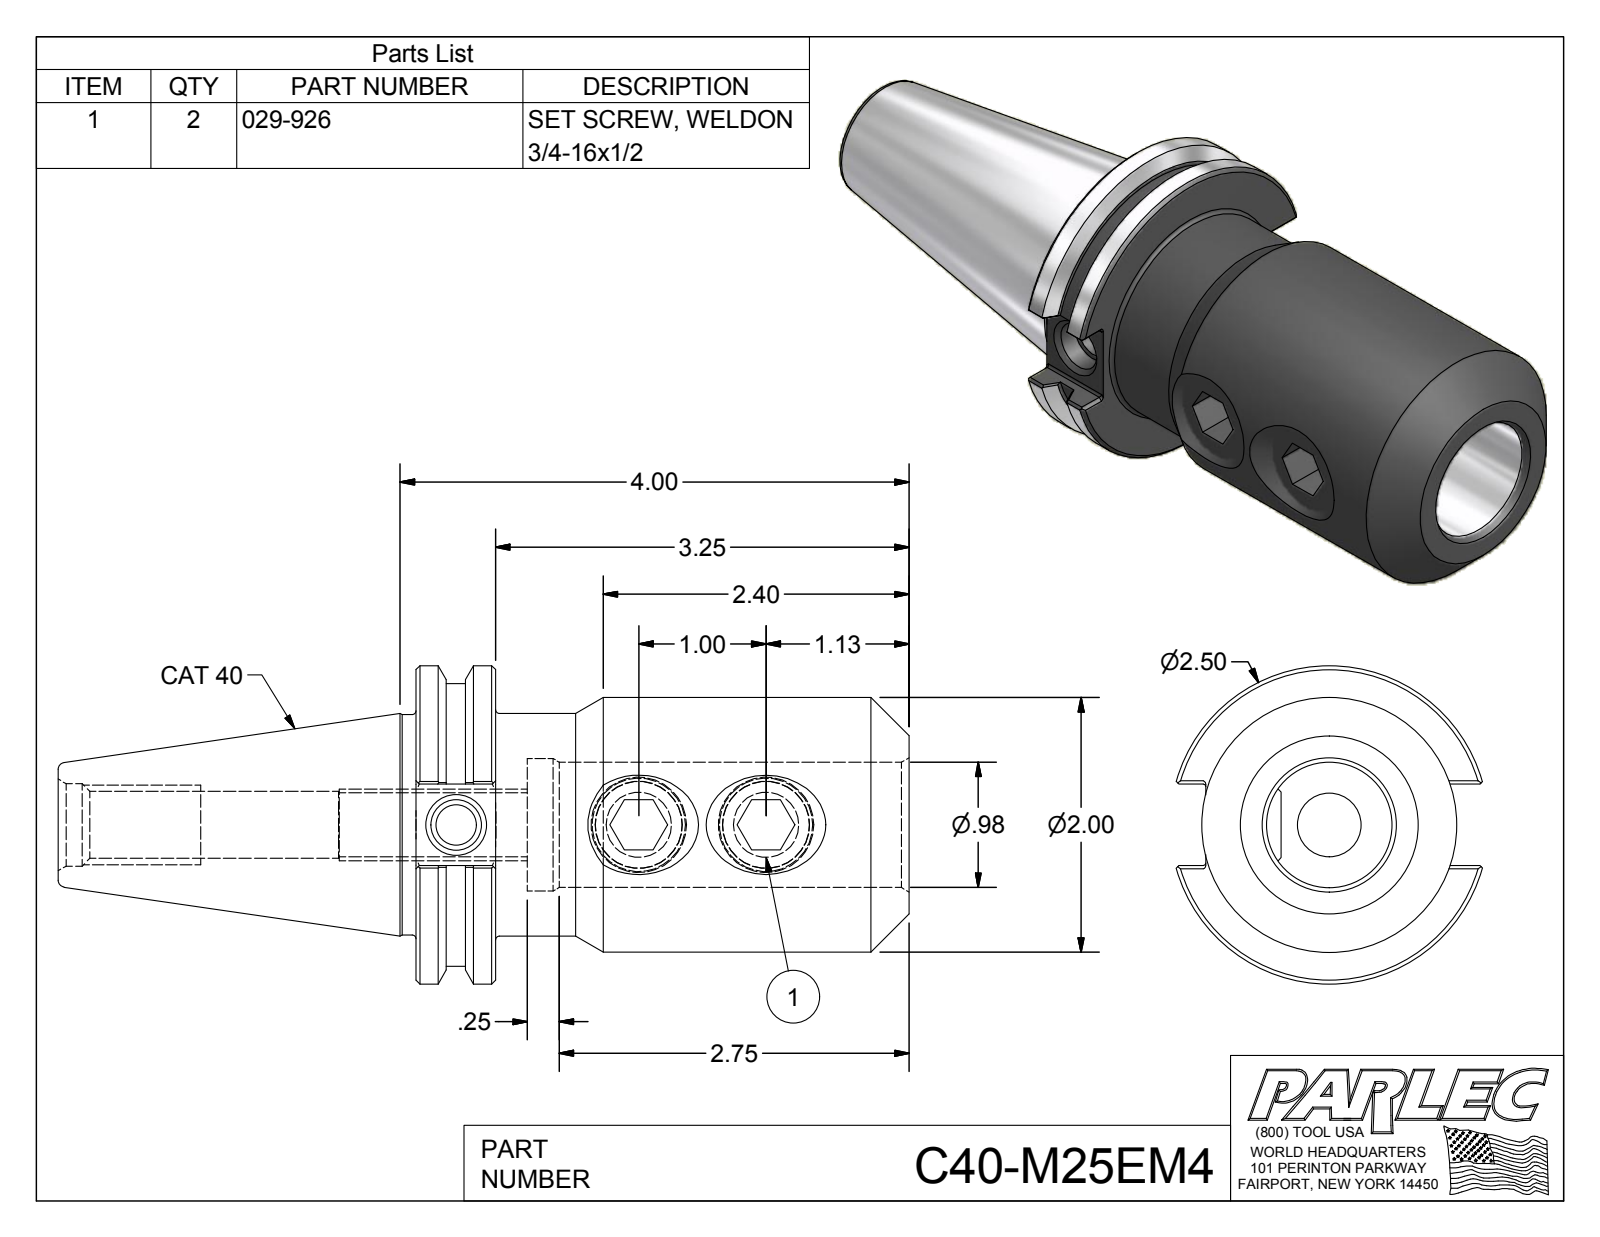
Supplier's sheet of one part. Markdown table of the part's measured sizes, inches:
| quantity | value |
| --- | --- |
| part name | C40-M25EM4; C40-M25EM4-1; 029-926 |
| STEP written by | Autodesk Inventor 2012 (AUTOMOTIVE_DESIGN) |
| units | inches |
| bodies | 3 solids, 118 faces (50 planar, 32 cylindrical, 36 other) |
| overall size | 6.687 × 2.5 × 2.406 |
| volume | 13.09 in³ |
| surface area | 66 in² |
| round holes (diameter × count) | 0.682 × 2, 0.315 × 1, 0.399 × 1, 0.502 × 1, 0.527 × 1, 0.648 × 1, 0.984 × 1, 1.04 × 1 |
| round bosses / shafts (diameter × count) | 0.75 × 2, 2.5 × 1, 2.219 × 1, 2 × 1, 1.75 × 1, 1.73 × 1 |
| partial cylindrical surfaces (radius × count) | 0.02 × 12 |
| main face-to-face distances | 0.625, 3.875, 3.25, 0.875, 0.25, 3, 0.394, 0.472, 0.866, 0.123 |
| hole center spacings | 1, 1.435, 2.435 |
